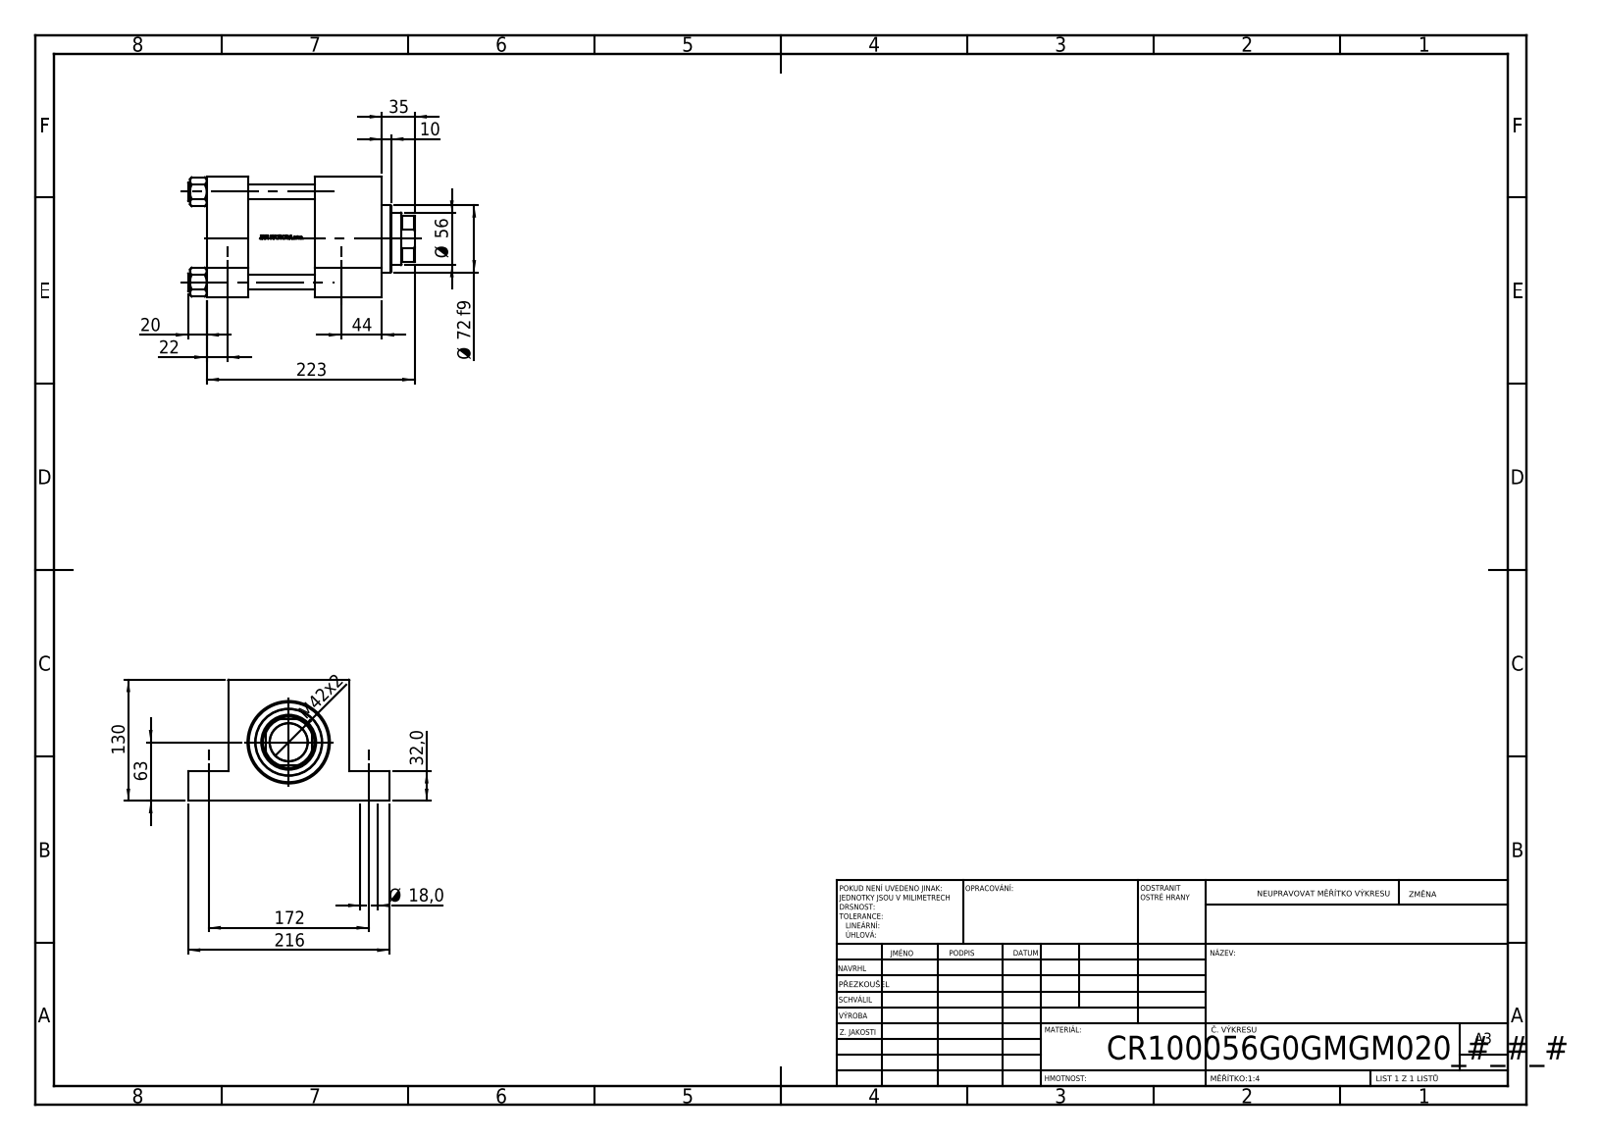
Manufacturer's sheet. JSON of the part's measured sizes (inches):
{"part_name": "V215CR_VCP_G; V215CR_G_TYCINKA; V215_VC_A; NUT_M5_G (+1 more)", "step_written_by": "SolidWorks 2019 (CONFIG_CONTROL_DESIGN)", "units": "inches", "bodies": {"solids": 11, "faces": 1135, "planar": 479, "cylindrical": 124, "other": 532}, "overall_size": [9.567, 8.504, 5.118], "volume_in3": 170.2, "surface_area_in2": 563.8, "round_holes": [[0.63, 4], [0.709, 4], [0.276, 2], [1.041, 2], [1.378, 2], [1.594, 1], [2.205, 1], [2.323, 1], [2.992, 1], [3.366, 1], [3.937, 1]], "round_bosses_or_shafts": [[0.748, 4], [4.173, 1], [2.835, 1]], "partial_cylinders_radius": [[1.063, 1]], "face_to_face_distances": [5.118, 1.772, 7.402, 5.63, 4.567, 2.795, 2.835, 1.26, 3.858, 1.693], "hole_center_spacings": [3.815, 2.643, 2.754, 4.803, 5.395, 6.772, 8.302, 4.665]}
